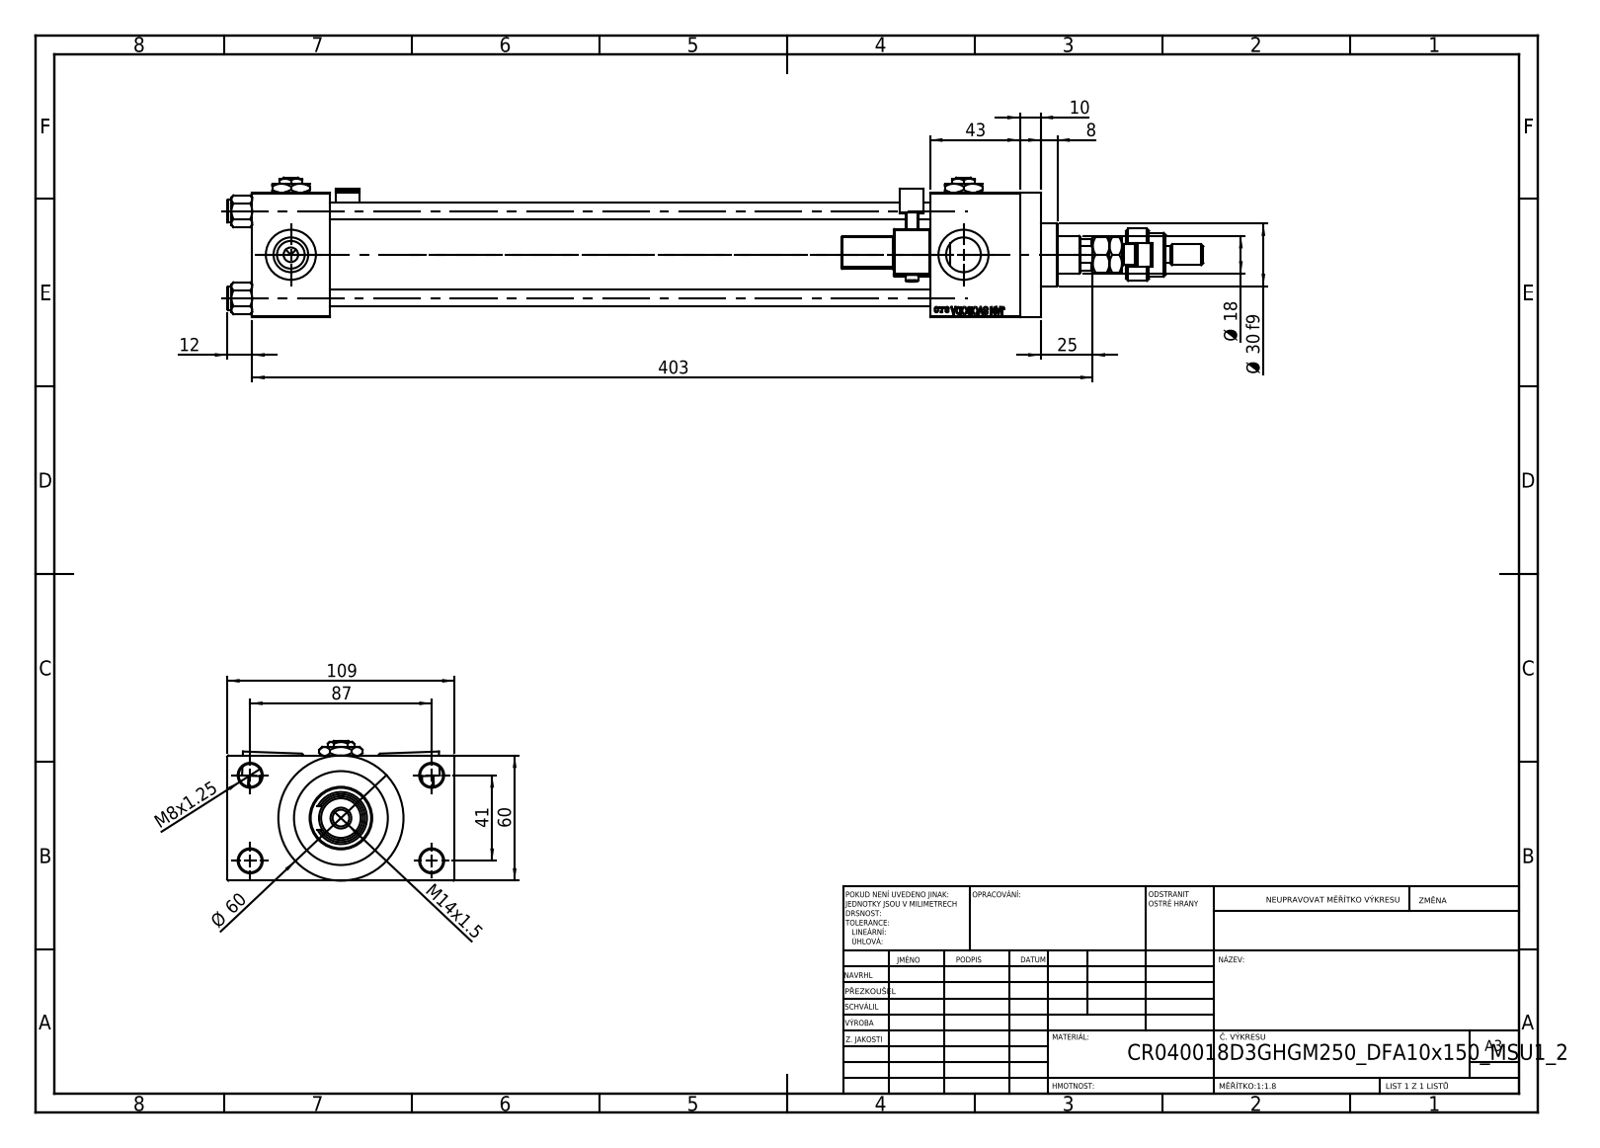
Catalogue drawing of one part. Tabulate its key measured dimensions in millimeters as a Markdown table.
| quantity | value |
| --- | --- |
| part name | V215CR_D_TYCINKA; V215CR_D_Body; NUT_M5_D; V215_VC_A (+5 more) |
| STEP written by | SolidWorks 2019 (CONFIG_CONTROL_DESIGN) |
| units | millimeters |
| bodies | 17 solids, 1444 faces (632 planar, 172 cylindrical, 640 other) |
| overall size | 468 × 109 × 67 |
| volume | 760 951 mm³ |
| surface area | 240 993 mm² |
| round holes (diameter × count) | 8 × 4, 11 × 4, 16.66 × 4, 24 × 4, 7 × 3, 8.5 × 1, 18 × 1, 21 × 1, 31 × 1, 40 × 1, 45 × 1 |
| round bosses / shafts (diameter × count) | 11 × 4, 6 × 2, 60 × 1, 46 × 1, 30 × 1, 25 × 1, 16 × 1, 10 × 1 |
| partial cylindrical surfaces (radius × count) | 0.5 × 48, 1 × 2, 2.5 × 2, 4 × 2, 5.5 × 1, 8.5 × 1, 8.75 × 1 |
| main face-to-face distances | 60, 288, 24.5, 84.5, 37, 325, 43, 368, 331, 10 |
| hole center spacings | 22.65, 29.49, 41.7, 47.15, 48.09, 64.35, 76.49, 41 |
